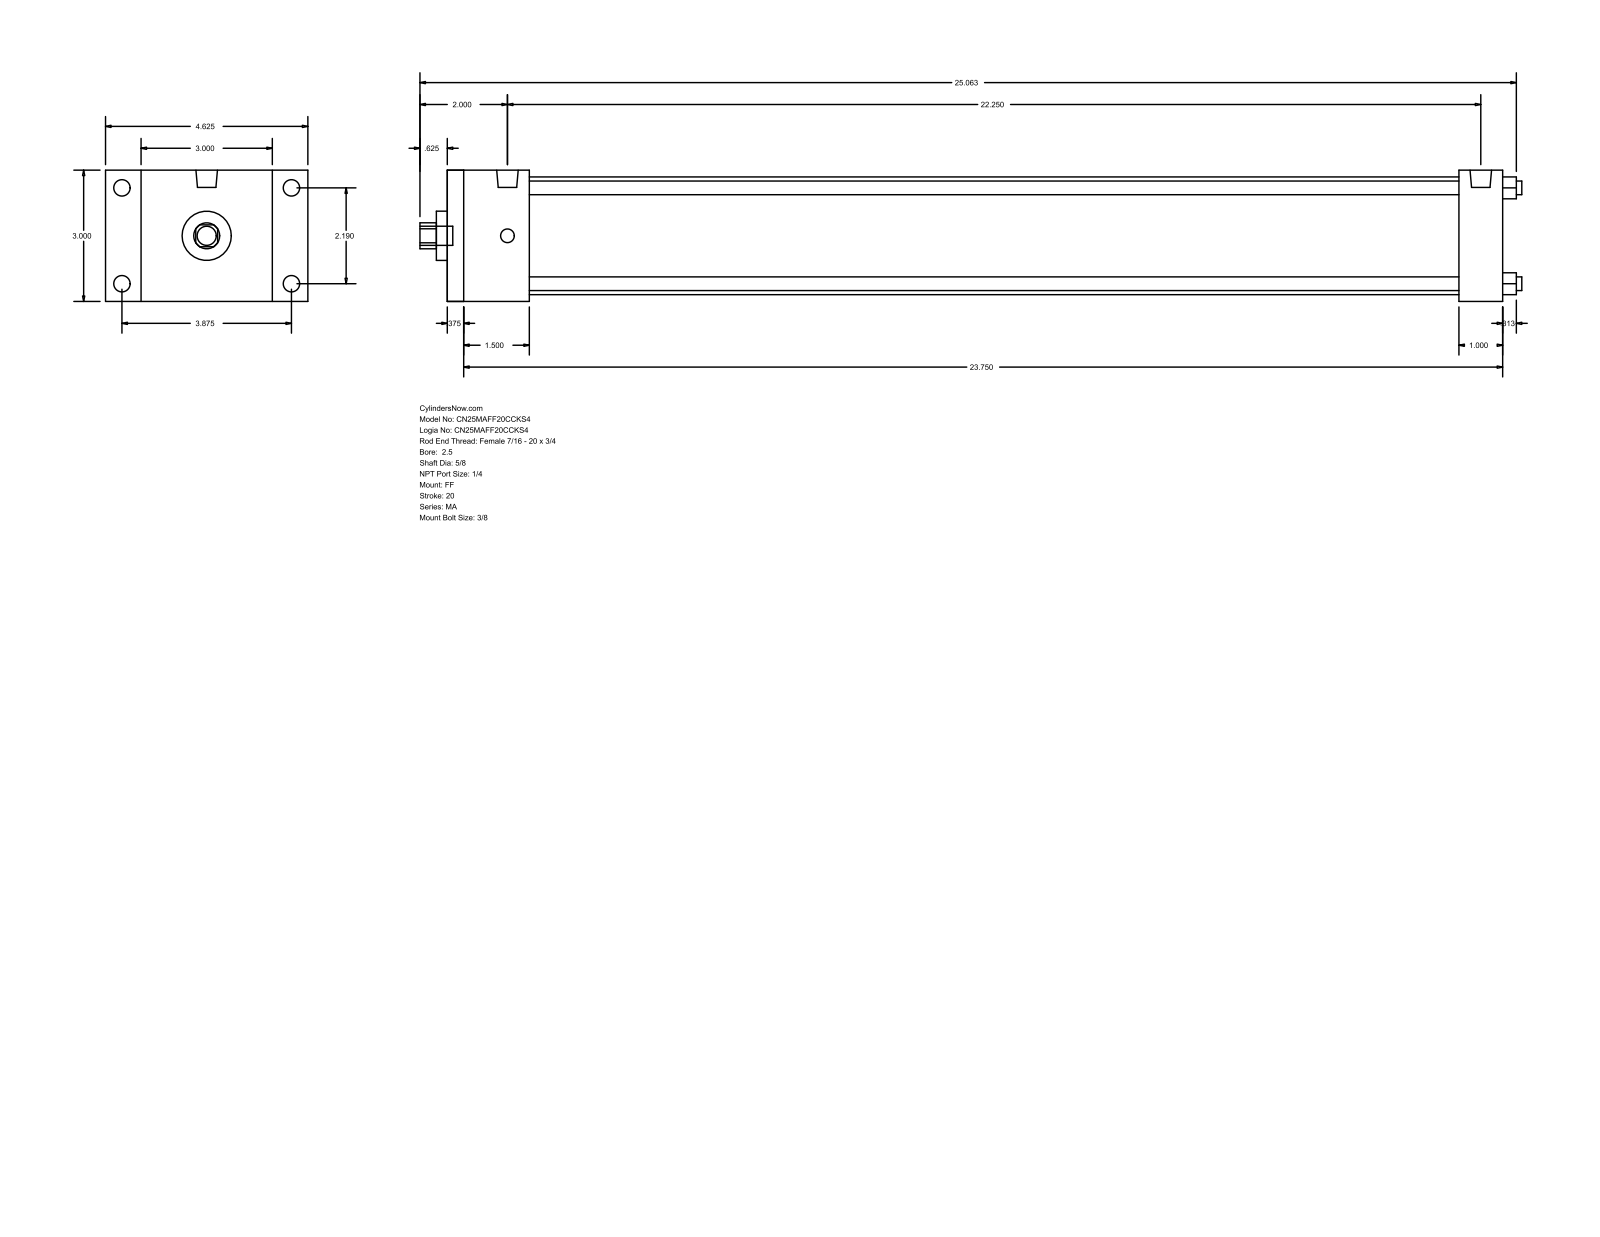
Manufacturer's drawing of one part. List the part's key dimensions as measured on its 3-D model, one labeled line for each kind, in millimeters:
Part name (STEP PRODUCT): MA_FF__0250_0.625
STEP written by: GSSL Pune (CONFIG_CONTROL_DESIGN)
Units: millimetres
Bodies: 0 solids, 92 faces (64 planar, 28 cylindrical, 0 other)
Overall size (bounding box): 639.76 × 117.47 × 76.2
Round holes (diameter × count): ⌀7.94 ×4, ⌀15.88 ×1, ⌀28.57 ×1, ⌀68.33 ×1
Round bosses / shafts (diameter × count): ⌀9.53 ×4, ⌀7.94 ×4, ⌀12.49 ×2, ⌀11.11 ×1
Partial cylindrical surfaces — rounded edges, fillets, slot ends (radius × count): R7.54 ×1
Main face-to-face distances: 76.2, 612.77, 9.52, 603.25, 25.4, 47.62, 587.37, 38.1, 577.85, 539.75
Hole centre spacings: 39.33, 55.62, 78.66
